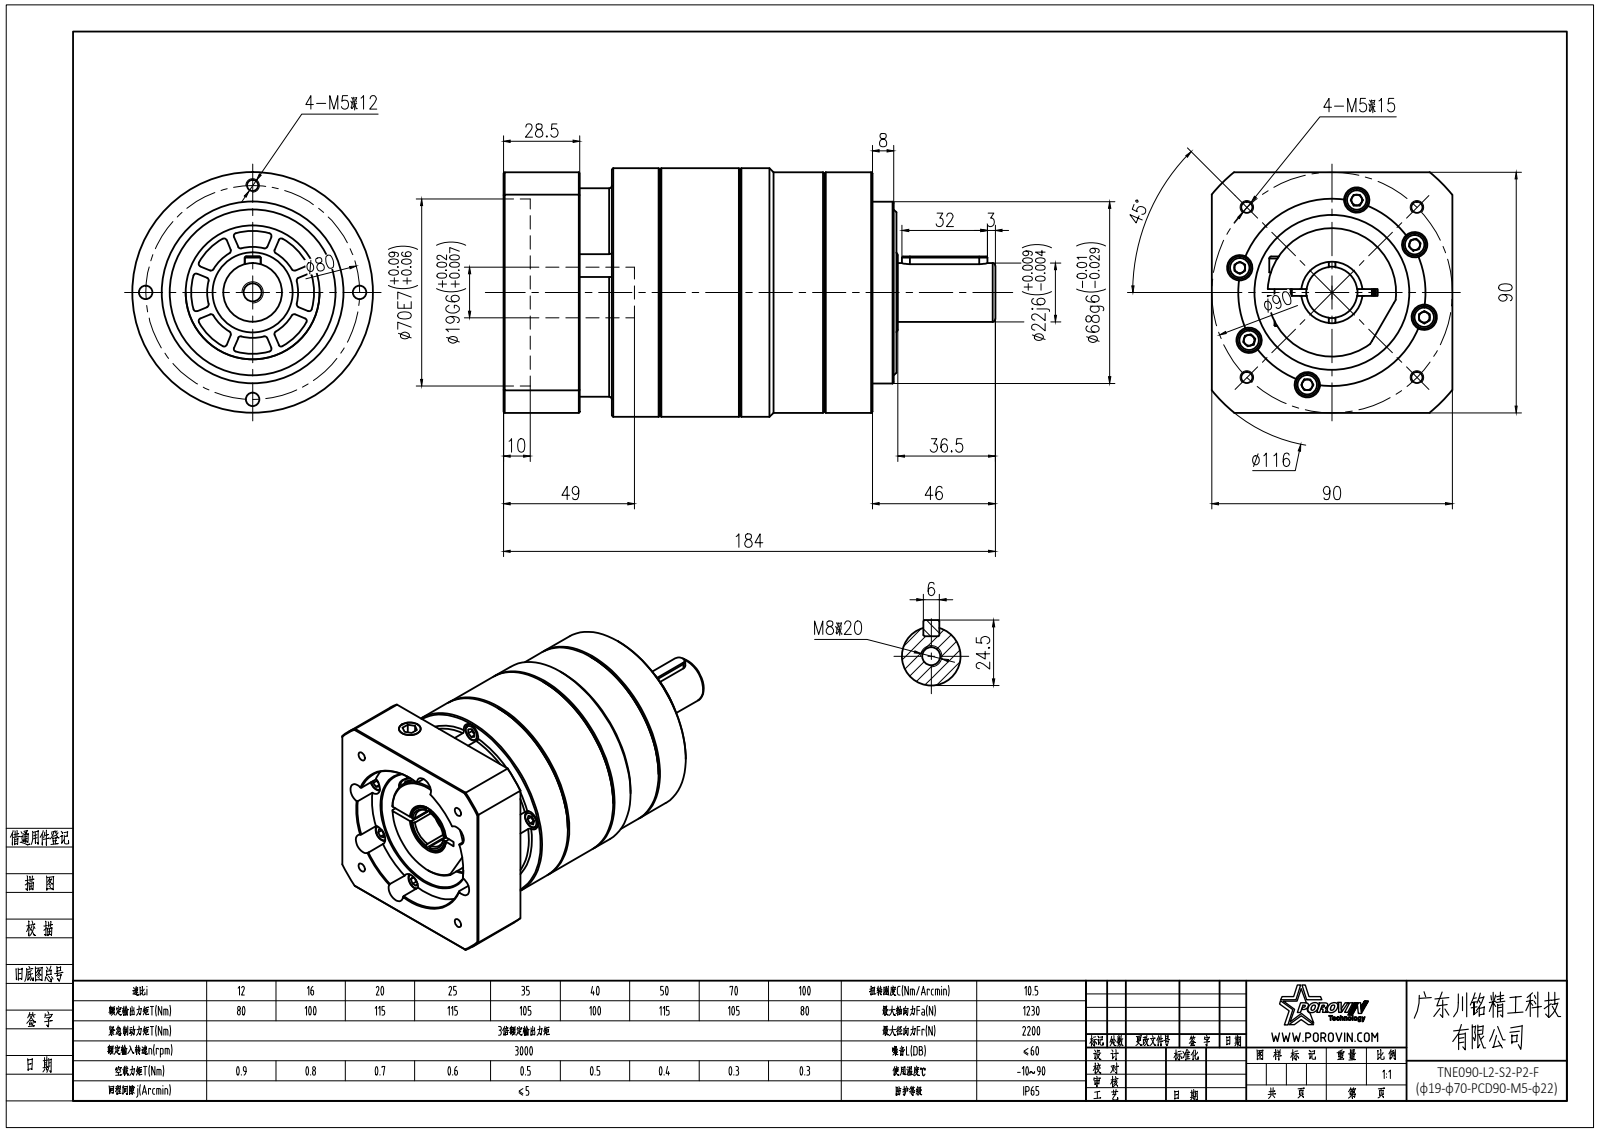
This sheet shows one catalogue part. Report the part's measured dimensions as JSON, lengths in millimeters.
{"part_name": "一级齿圈外形图 KE90; spring lock washers--normal type gb_GB_FASTENER_WASHER_SW 5; hexagon socket head cap screws gb_GB_FASTENER_SCREWS_HSHCS M5X20-N; hexagon socket head cap screws gb_GB_FASTENER_SCREWS_HSHCS M6X20-N (+2 more)", "step_written_by": "SolidWorks 2016 (CONFIG_CONTROL_DESIGN)", "units": "millimeters", "bodies": {"solids": 30, "faces": 856, "planar": 337, "cylindrical": 319, "other": 200}, "overall_size": [184, 93, 93], "volume_mm3": 797680, "surface_area_mm2": 151667, "round_holes": [[4.2, 10], [5.4, 10], [5.5, 10], [9.5, 10], [5, 5], [6.5, 1], [6.8, 1], [8.5, 1], [10.2, 1], [19, 1], [19.2, 1], [50, 1]], "round_bosses_or_shafts": [[8.5, 10], [8, 10], [5, 10], [93, 1], [90, 1], [78.5, 1], [78, 1], [68, 1]], "partial_cylinders_radius": [[1, 32], [3, 2], [5.5, 1], [23, 1], [35, 1], [58, 1]], "face_to_face_distances": [30, 31.5, 61.5, 88.5, 58.5, 32.5, 28.5, 90, 2.5, 94], "hole_center_spacings": [32.85, 78.55, 35.75, 75.85, 10.75, 22.73, 33.05, 40]}
